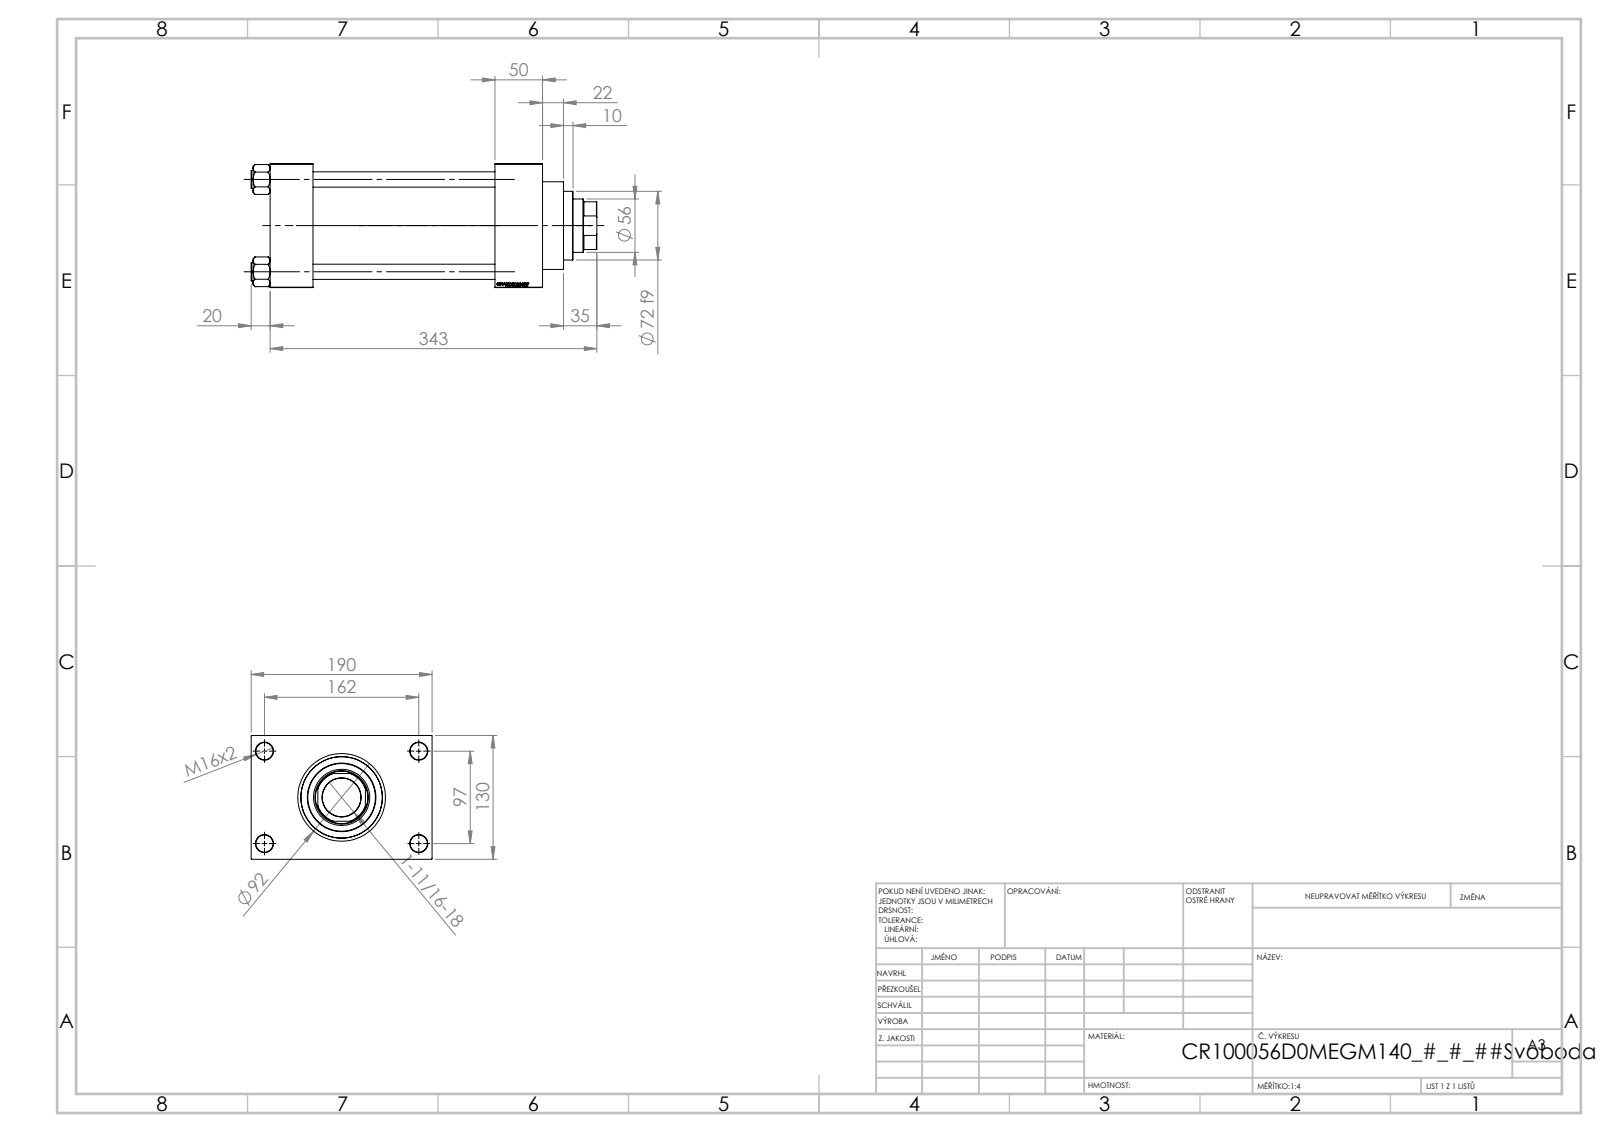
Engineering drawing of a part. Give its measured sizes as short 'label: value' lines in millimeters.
name: V215_VC_A; NUT_M5_D; V215CR_VCP_D; V215CR_D_Body (+1 more)
written by: SolidWorks 2019 (CONFIG_CONTROL_DESIGN)
unit: mm
bodies: 11 solids, 1152 faces (545 planar, 89 cylindrical, 518 other)
size: 363 × 190 × 130
volume: 3 153 000 mm³; area: 482 773 mm²
holes: 4× ⌀16, 4× ⌀18, 2× ⌀7, 2× ⌀26.44, 2× ⌀35, 1× ⌀40.5, 1× ⌀56, 1× ⌀59, 1× ⌀76, 1× ⌀85.5, 1× ⌀100
bosses: 4× ⌀19, 1× ⌀106, 1× ⌀92, 1× ⌀72
rounds: 1× R27
face distances: 130, 50, 45, 236, 191, 286, 241, 190, 30, 160
hole spacings: 32.55, 68.52, 94.41, 96.9, 102.27, 129.45, 161.73, 97
